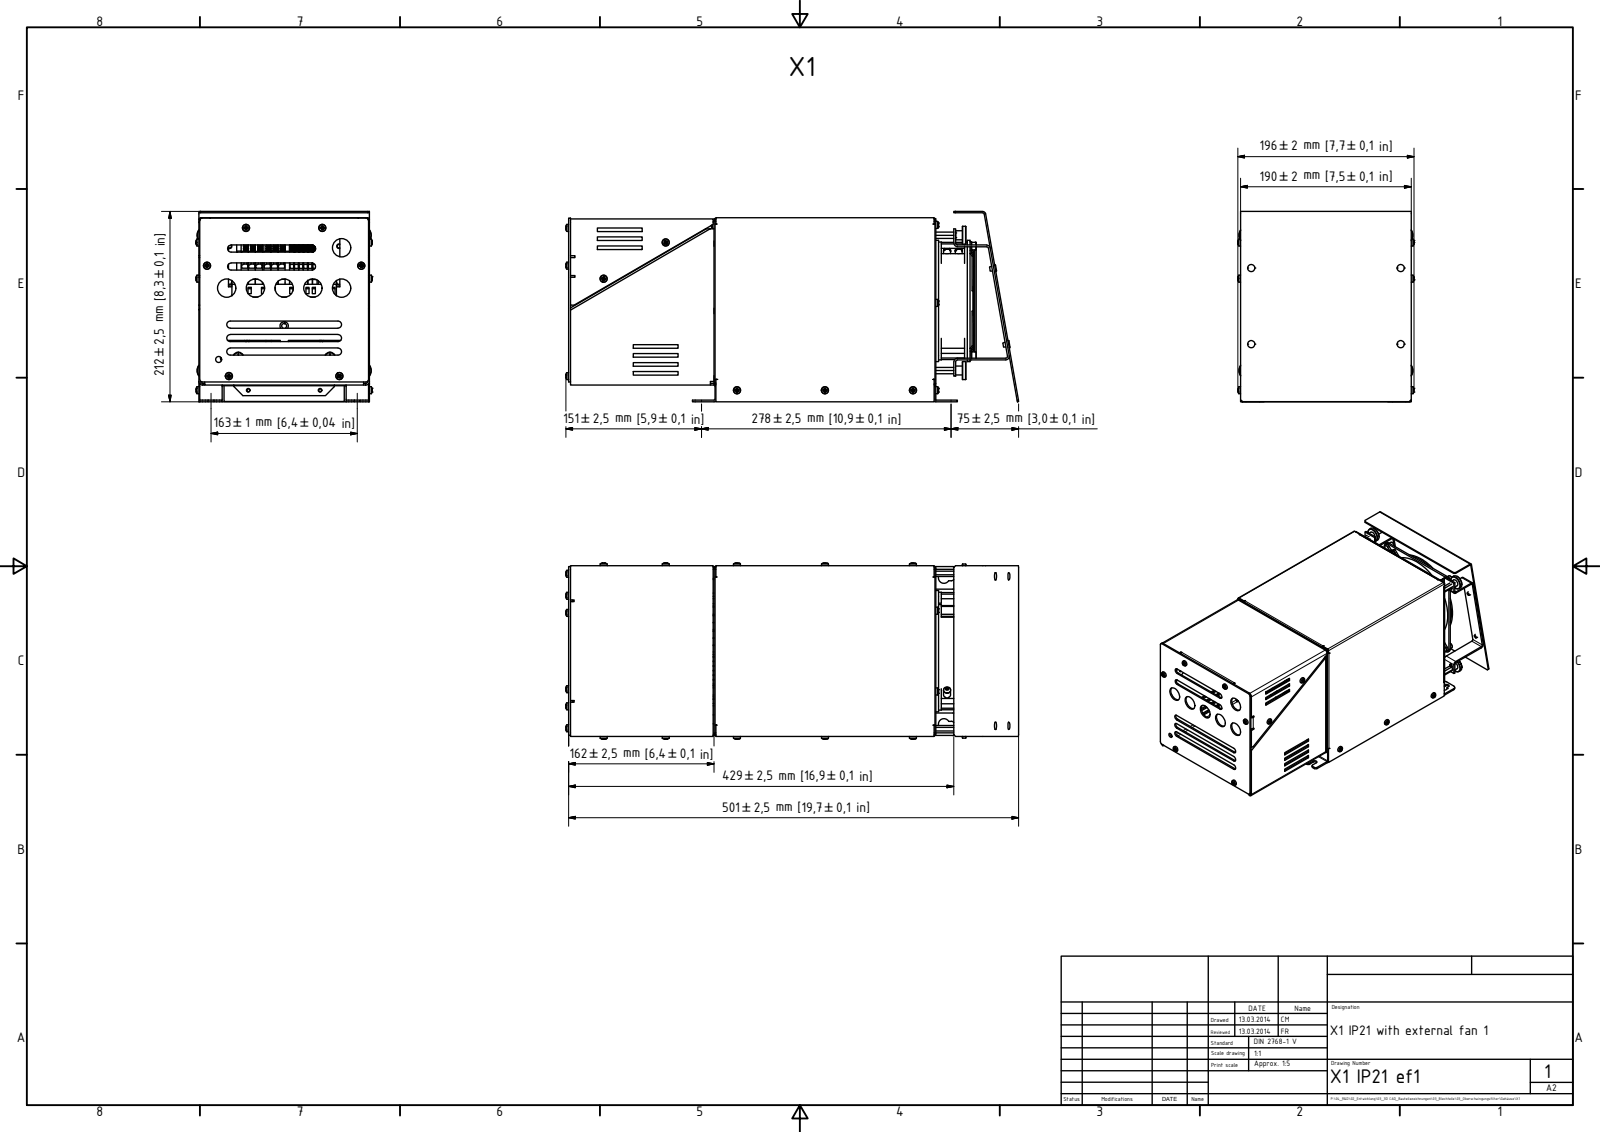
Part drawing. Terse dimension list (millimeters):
name: 10100282 Bodenblech RHF-BG X1; 10100383 Deckel RHF-BG X1-A; 10100382 Anschlussblech RHF-BG X1; 10100363 Lüfterblech RHF-BG X1 (+8 more)
written by: Autodesk Inventor 2015 (AUTOMOTIVE_DESIGN)
unit: mm
bodies: 125 solids, 8160 faces (5026 planar, 2146 cylindrical, 988 other)
size: 504.39 × 212 × 196.23
volume: 1 090 000 mm³; area: 1 275 000 mm²
holes: 29× ⌀5, 23× ⌀3.24, 22× ⌀4, 12× ⌀4.72, 11× ⌀4.2, 8× ⌀3.5, 8× ⌀6, 7× ⌀5.4, 6× ⌀4.13, 6× ⌀5.3, 6× ⌀20.5, 5× ⌀6.5
bosses: 29× ⌀4, 24× ⌀1.5, 21× ⌀3.65, 10× ⌀10, 9× ⌀9.2, 5× ⌀5, 4× ⌀20, 4× ⌀8.5
rounds: 69× R2, 56× R0.5, 43× R1, 35× R3, 34× R0.75, 32× R0.15, 26× R4, 24× R0.45
face distances: 1, 2, 188, 189, 187, 190, 185, 186, 246, 0.7
hole spacings: 5.1, 23.56, 10.2, 23, 25.16, 166.5, 15.3, 27.62
